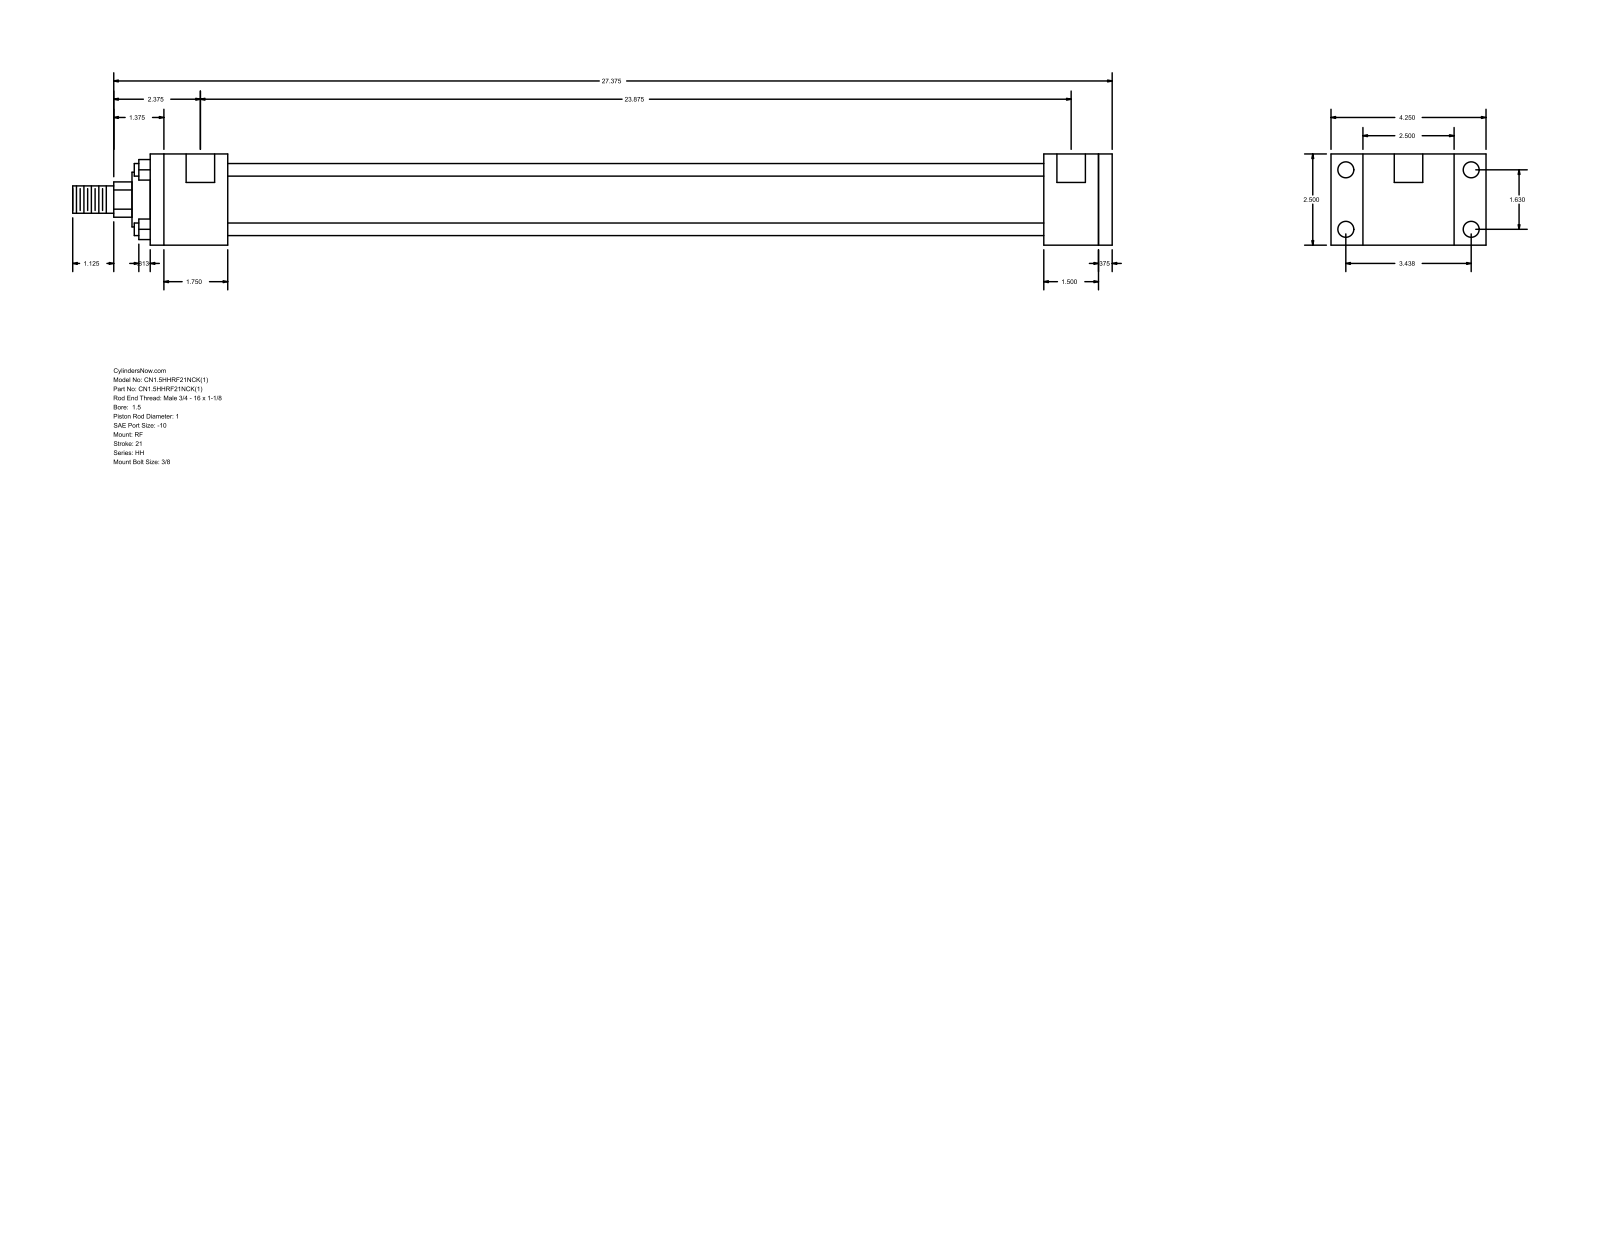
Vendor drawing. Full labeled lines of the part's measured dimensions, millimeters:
Part name (STEP PRODUCT): HH_RF__0150_1
STEP written by: GSSL Pune (CONFIG_CONTROL_DESIGN)
Units: millimetres
Bodies: 0 solids, 92 faces (64 planar, 28 cylindrical, 0 other)
Overall size (bounding box): 723.9 × 107.95 × 63.5
Round holes (diameter × count): ⌀5.56 ×4, ⌀11.13 ×4, ⌀19.84 ×2
Round bosses / shafts (diameter × count): ⌀8.76 ×4, ⌀44.45 ×1, ⌀38.1 ×1, ⌀25.4 ×1, ⌀19.05 ×1
Partial cylindrical surfaces — rounded edges, fillets, slot ends (radius × count): R12.29 ×1
Main face-to-face distances: 63.5, 9.53, 38.1, 568.32, 606.42, 615.95, 47.63, 53.98, 622.3, 660.4
Hole centre spacings: 1.59, 41.4, 87.32, 96.64, 608.01, 609.6, 606.42
